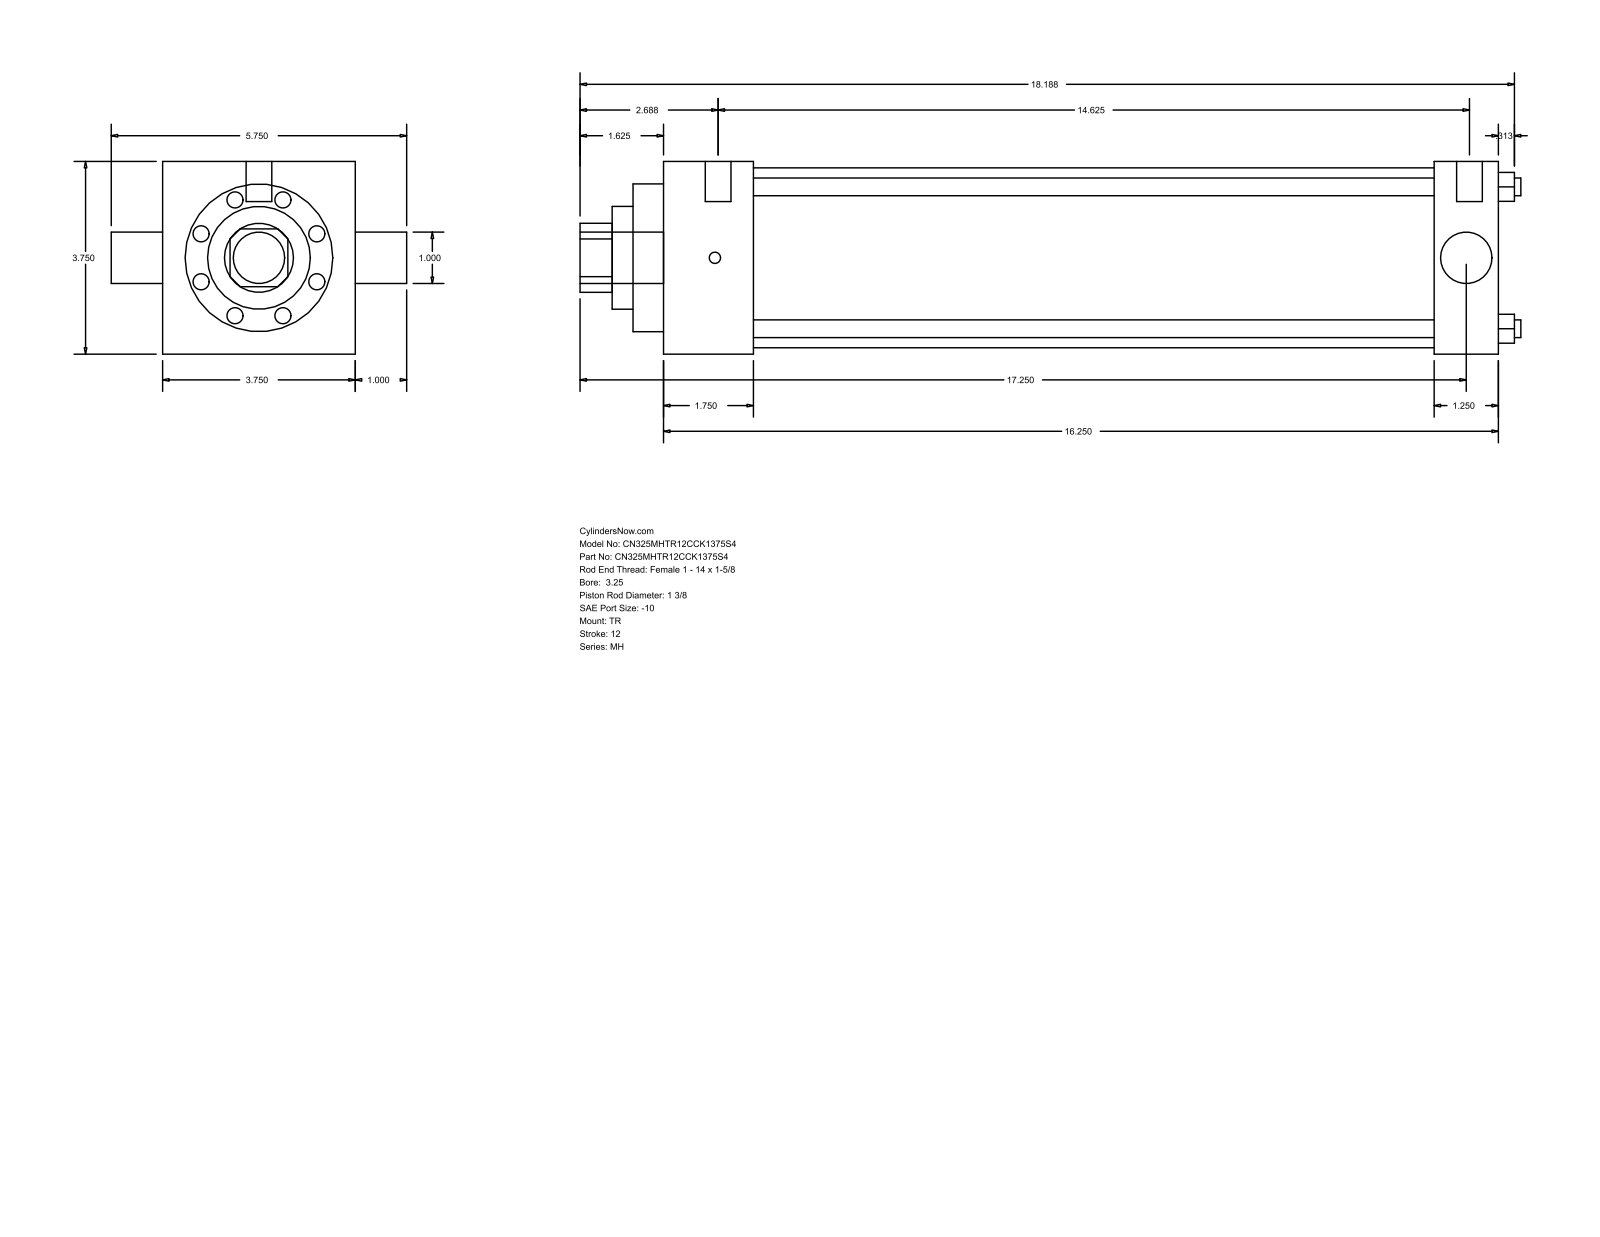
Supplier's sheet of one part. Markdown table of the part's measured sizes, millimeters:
| quantity | value |
| --- | --- |
| part name | MH_TR__0325_1.375 |
| STEP written by | GSSL Pune (CONFIG_CONTROL_DESIGN) |
| units | millimeters |
| bodies | 0 solids, 86 faces (61 planar, 25 cylindrical, 0 other) |
| overall size | 465.14 × 146.05 × 95.25 |
| round holes (diameter × count) | 8.76 × 4, 25.4 × 1, 34.92 × 1, 50.8 × 1, 73.03 × 1, 88.9 × 1 |
| round bosses / shafts (diameter × count) | 5.56 × 3, 12.7 × 2, 25.4 × 1 |
| partial cylindrical surfaces (radius × count) | 17.06 × 1 |
| main face-to-face distances | 95.24, 412.75, 44.45, 381, 336.55, 368.3, 31.75, 15.08, 59.53, 396.08 |
| hole center spacings | 49.57, 70.1, 99.14 |
